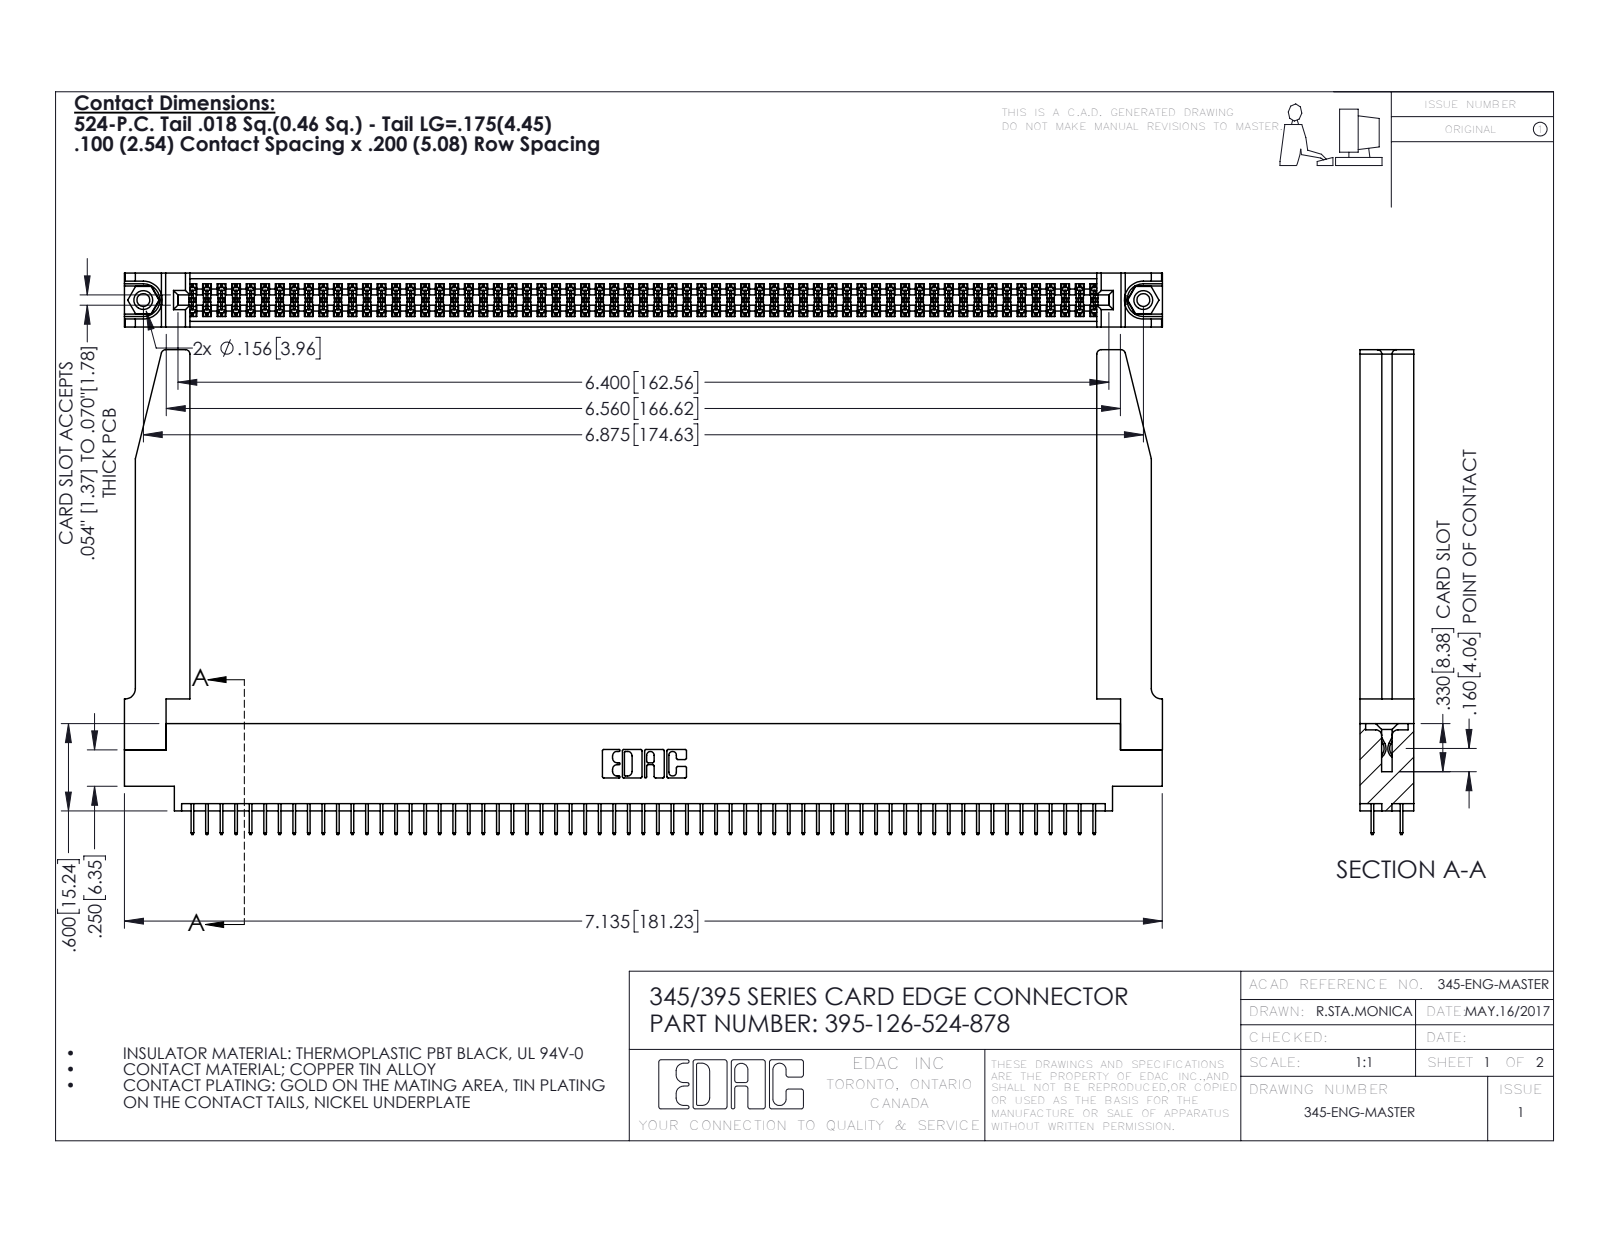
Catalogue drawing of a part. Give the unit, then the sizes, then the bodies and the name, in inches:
Units: inches
Overall size (bounding box): 7.136 × 3.332 × 0.37
Round holes (diameter × count): ⌀0.089 ×2, ⌀0.125 ×2, ⌀0.156 ×2, ⌀0.064 ×1
Round bosses / shafts (diameter × count): ⌀0.155 ×2
Partial cylindrical surfaces — rounded edges, fillets, slot ends (radius × count): R0.006 ×189, R0.01 ×22, R0.03 ×8, R0.007 ×6, R0.031 ×6, R0.026 ×3, R0.014 ×2, R0.019 ×2
Main face-to-face distances: 0.072, 0.37, 0.298, 0.2, 0.098, 0.272, 0.025, 0.225, 0.072, 0.175
Hole centre spacings: 0.27, 6.639, 6.875
Volume: 1.542 in³ · Surface area: 50.76 in²
Bodies: 131 solids, 7168 faces (5140 planar, 1976 cylindrical, 52 other)
Part name (STEP PRODUCT): 345-250-001_345-250-001-102; 345 Part_0.170 Offset - 0.156 Dia-TH; 395-126-524-878; 345-220-078_345-220-078 (+1 more)
STEP written by: SolidWorks 2016 (CONFIG_CONTROL_DESIGN)
